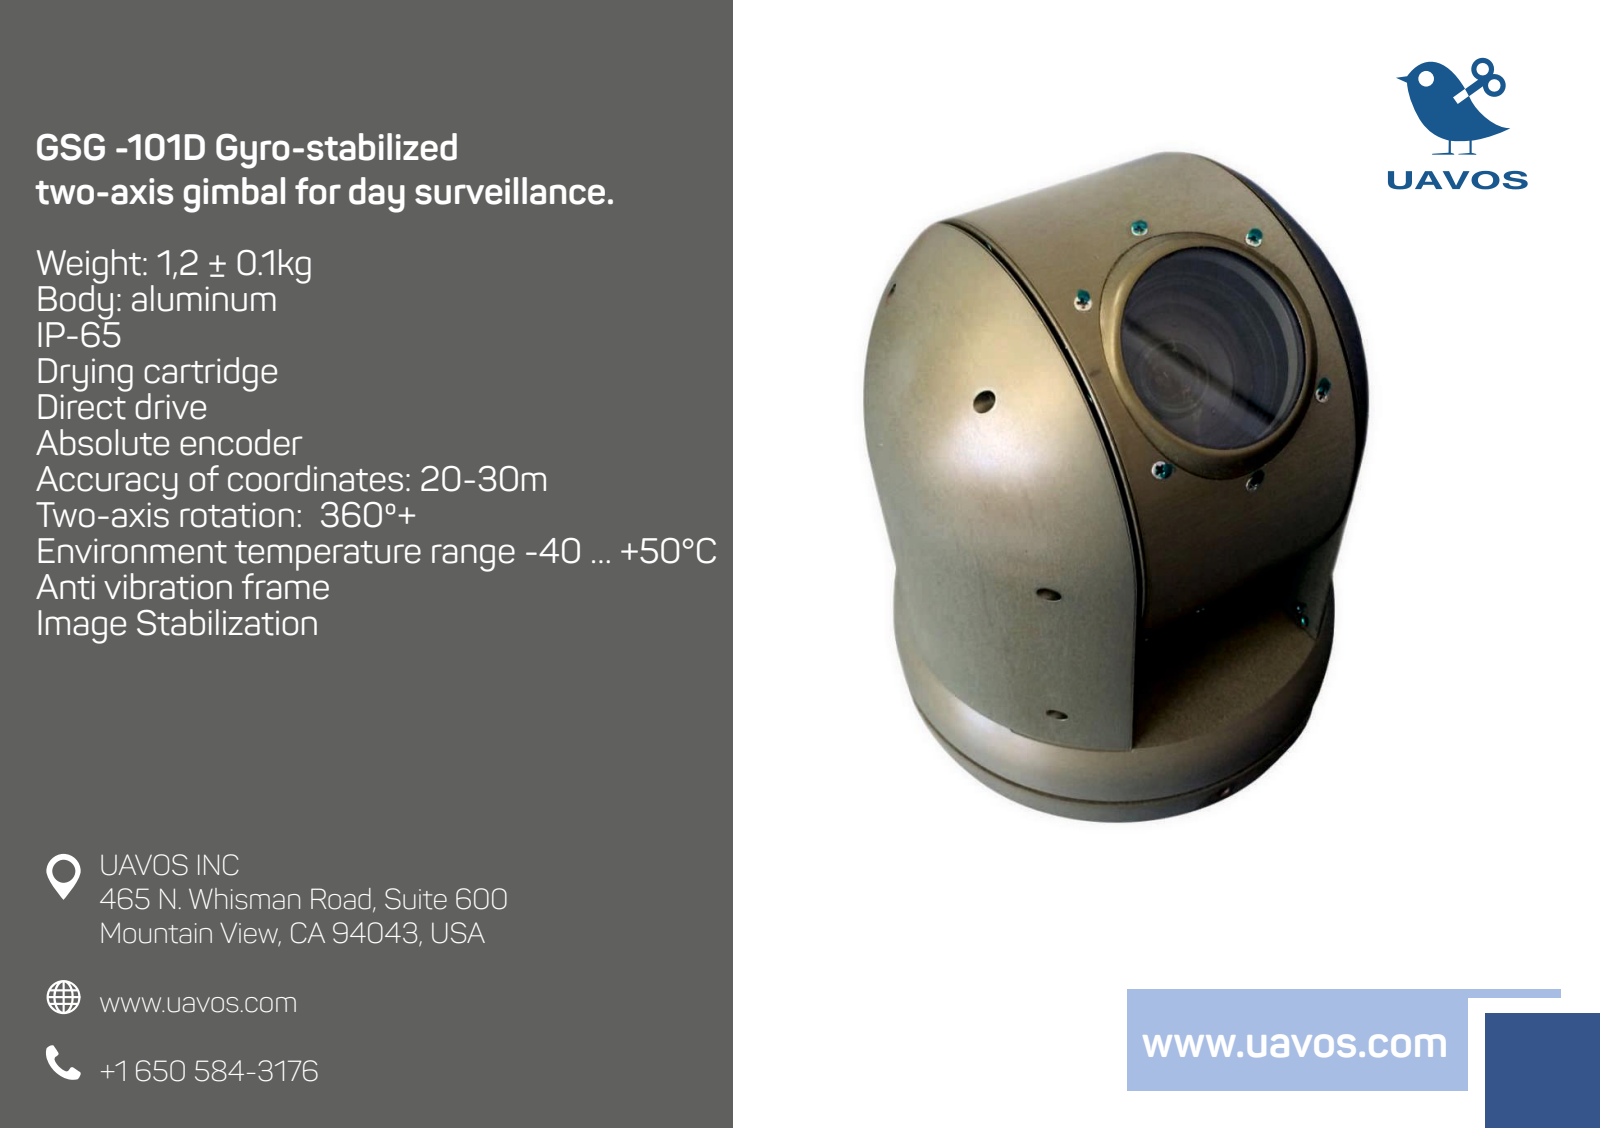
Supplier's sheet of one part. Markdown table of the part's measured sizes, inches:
| quantity | value |
| --- | --- |
| part name | ДИСК АЗИМУТА ПОД УГЛУБЛЕННЫЙ МОТОР1_2; Влагопоглотитель м14 короткий; КОЖУХ УГЛАМЕСТА1; центр барабан глугой (+8 more) |
| STEP written by | SolidWorks 2017 (AUTOMOTIVE_DESIGN) |
| units | inches |
| bodies | 29 solids, 2709 faces (1176 planar, 1381 cylindrical, 152 other) |
| overall size | 6.1 × 5.591 × 5.591 |
| volume | 68.96 in³ |
| surface area | 735.4 in² |
| round holes (diameter × count) | 0.079 × 85, 0.118 × 21, 0.039 × 10, 0.098 × 8, 0.063 × 6, 0.157 × 6, 0.213 × 6, 0.094 × 4, 0.181 × 4, 0.094 × 2, 0.138 × 2, 0.787 × 2 |
| round bosses / shafts (diameter × count) | 0.126 × 18, 0.118 × 18, 0.044 × 8, 0.134 × 6, 0.197 × 5, 0.177 × 4, 0.11 × 4, 2.205 × 2 |
| partial cylindrical surfaces (radius × count) | 0.079 × 60, 0.063 × 24, 0.041 × 16, 0.118 × 14, 0.106 × 12, 0.024 × 8, 0.059 × 8, 0.073 × 8 |
| main face-to-face distances | 0.02, 0.091, 0.071, 0.051, 2.165, 0.031, 2.61, 0.394, 0.098, 0.992 |
| hole center spacings | 0.78, 0.551, 0.422, 1.019, 1.645, 1.803, 2.15, 2.219 |
